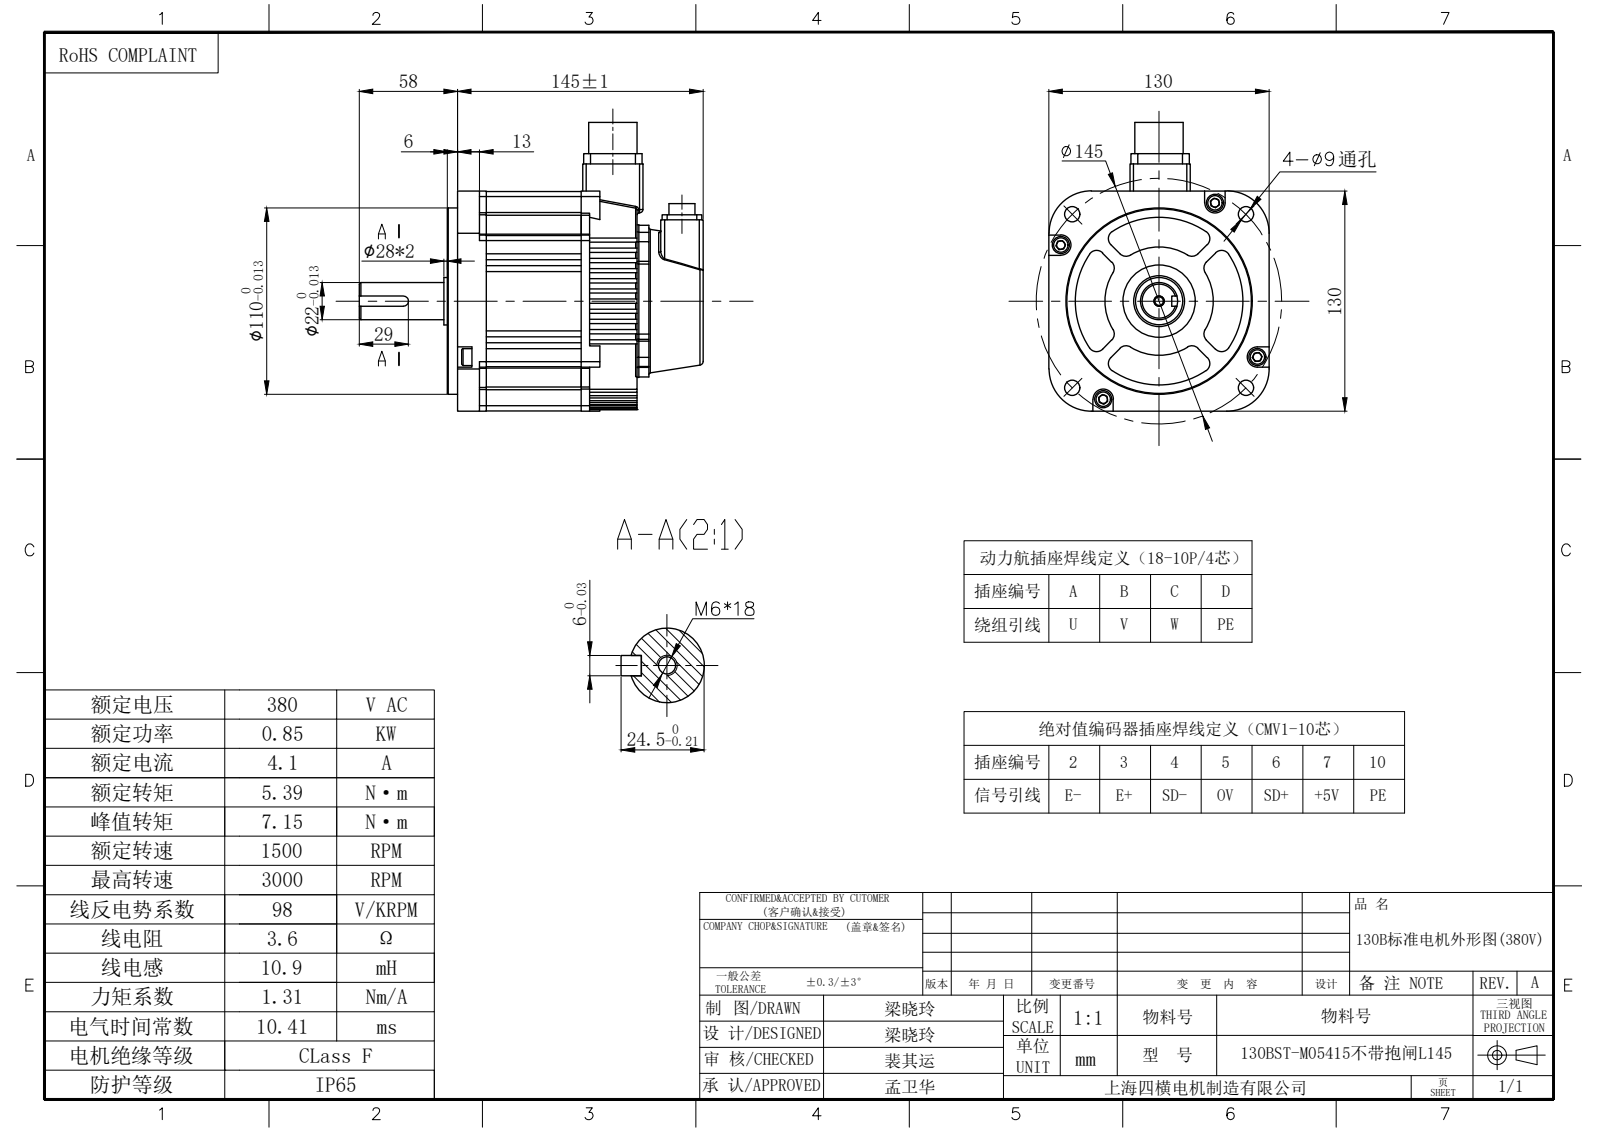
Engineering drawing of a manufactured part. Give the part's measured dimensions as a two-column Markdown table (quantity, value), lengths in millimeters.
| quantity | value |
| --- | --- |
| part name | 130BST后盖; 130BST-M08315前端盖出轴; 130BST机身56; hexagon socket head cap screws gb_ M6 (+2 more) |
| STEP written by | SolidWorks 2020 (AUTOMOTIVE_DESIGN) |
| units | millimeters |
| bodies | 44 solids, 798 faces (387 planar, 332 cylindrical, 79 other) |
| overall size | 203 × 170.5 × 130 |
| volume | 1 777 000 mm³ |
| surface area | 211 010 mm² |
| round holes (diameter × count) | 3 × 8, 6.6 × 8, 5 × 5, 9 × 4, 11.5 × 1, 24 × 1, 42.6 × 1 |
| round bosses / shafts (diameter × count) | 10 × 4, 6 × 4, 2.5 × 4, 110 × 1, 30 × 1, 28.5 × 1, 28 × 1, 22 × 1 |
| partial cylindrical surfaces (radius × count) | 1.5 × 16, 3.25 × 16, 5 × 16, 2 × 15, 3 × 13, 3.5 × 8, 2.25 × 4, 2.5 × 4 |
| main face-to-face distances | 56, 89, 33, 73, 17, 106, 72, 129.75, 3.5, 6 |
| hole center spacings | 1.34, 12.02, 17, 27, 47.91, 66.73, 68, 94.37 |
